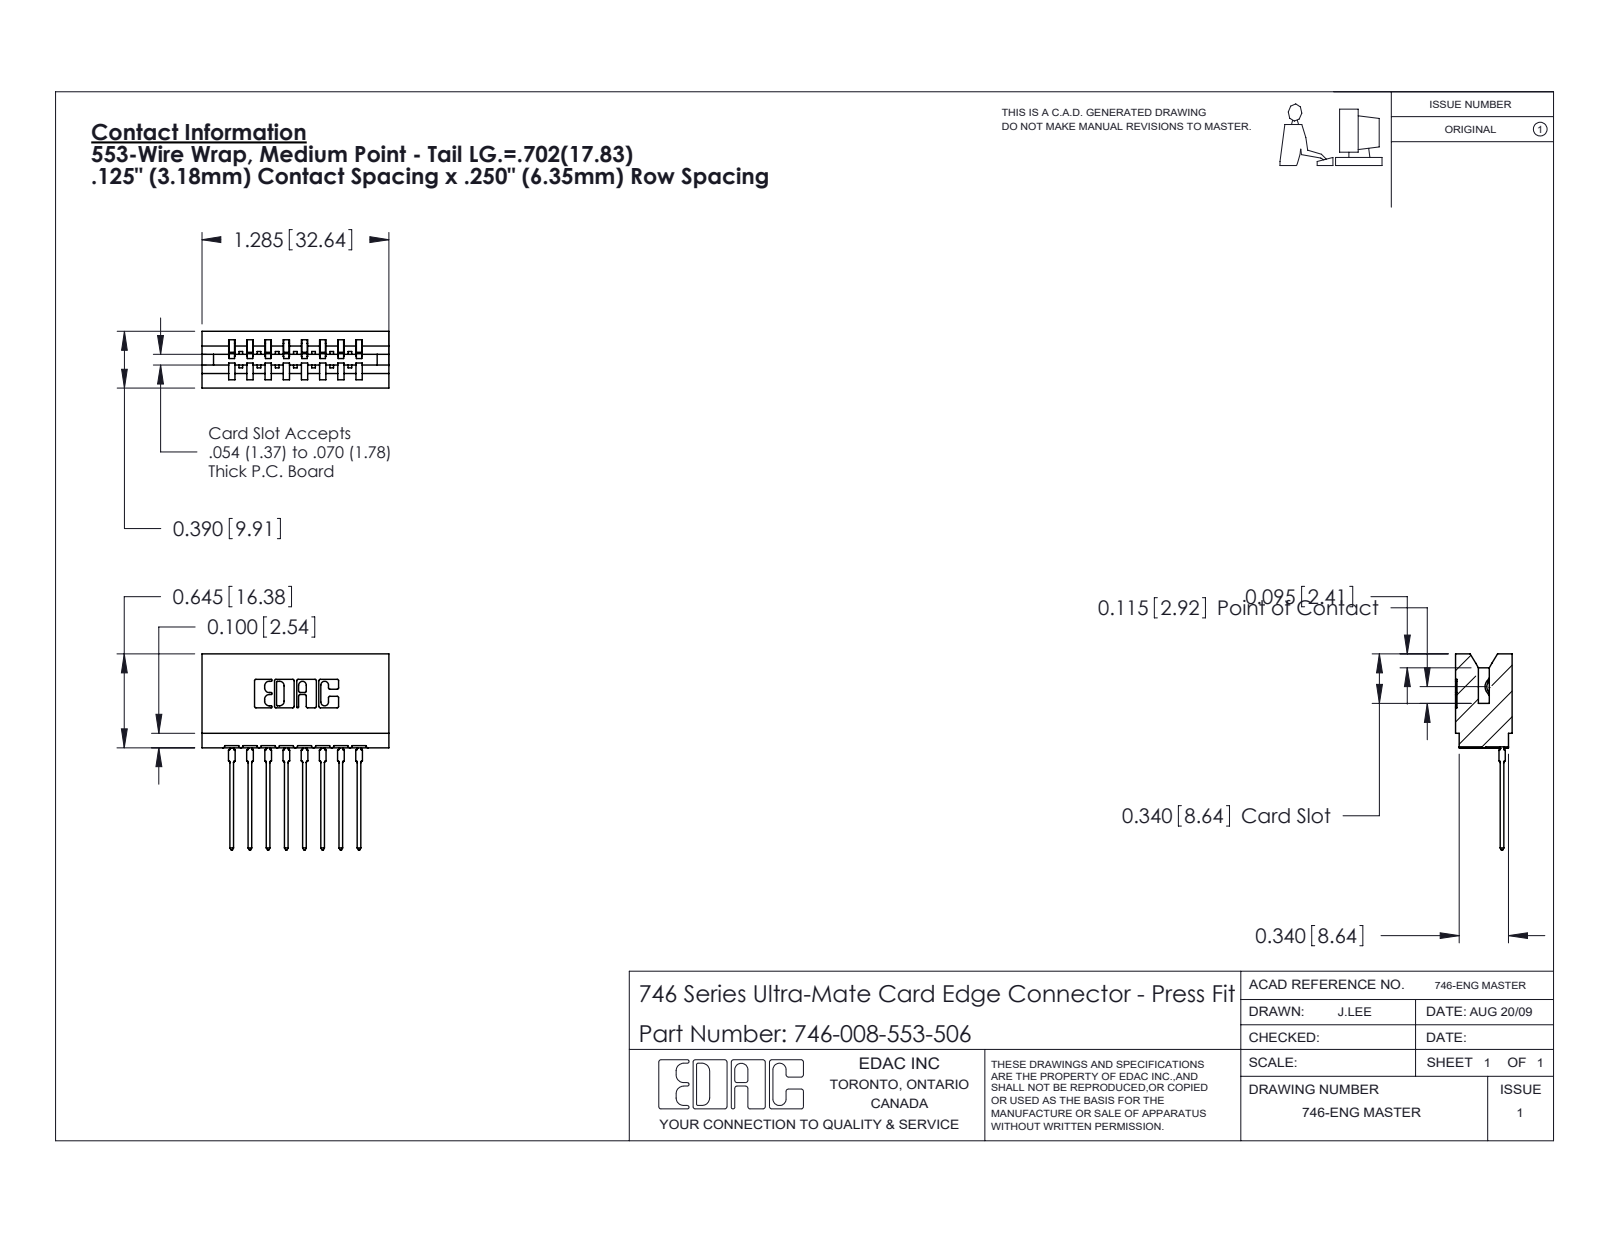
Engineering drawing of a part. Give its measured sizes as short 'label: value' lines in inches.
name: 746-008-553-506; 746-292-001_553; 746 Part_.340 Slot Depth - 06
written by: SolidWorks 2020 (CONFIG_CONTROL_DESIGN)
unit: in
bodies: 9 solids, 962 faces (560 planar, 194 cylindrical, 208 other)
size: 1.346 × 1.285 × 0.39
volume: 0.237 in³; area: 7.558 in²
rounds: 22× R0.01, 16× R0.021, 9× R0.015, 6× R0.007, 6× R0.031, 4× R0.005, 4× R0.011, 3× R0.026
face distances: 0.25, 0.042, 0.125, 0.5, 0.333, 0.057, 0.292, 0.375, 0.208, 0.125
